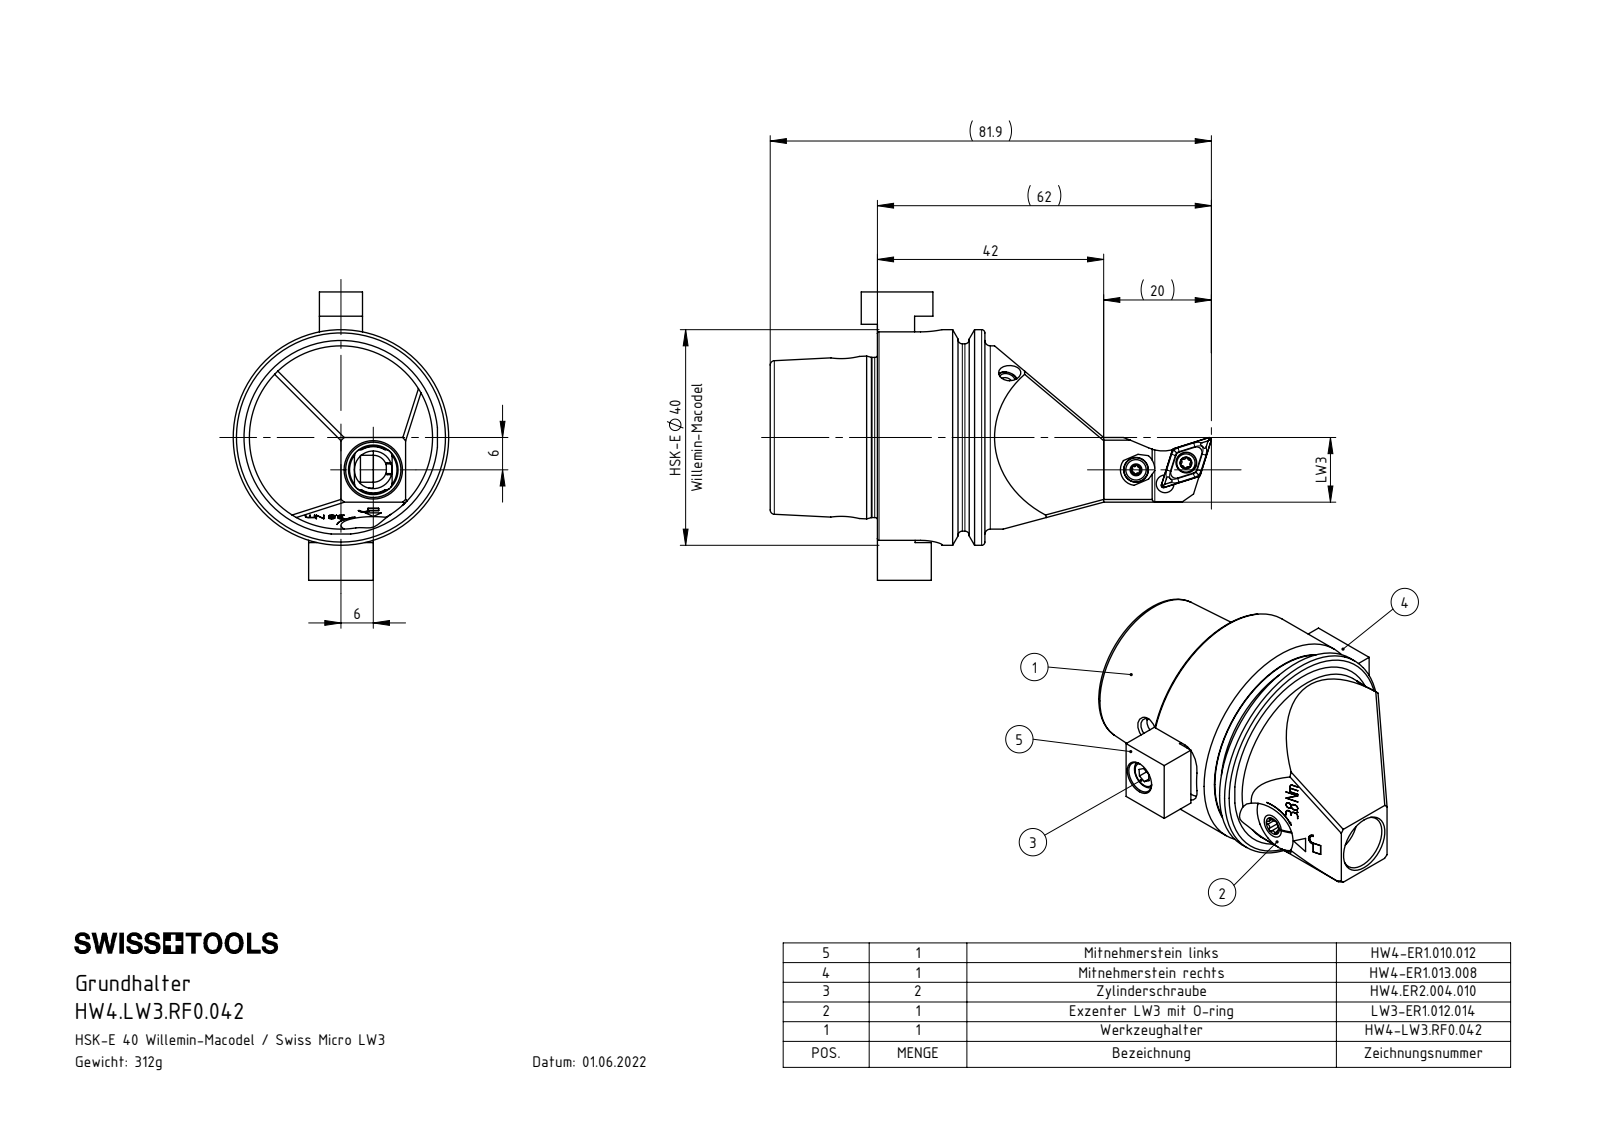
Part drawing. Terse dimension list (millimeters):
name: HW4-ER1.010.012_A; LW3-ER1.012.014_C_Standard<Wie bearbeitet>; HW4-ER2.004.010_A; HW4.LW3.RF0.042 (+5 more)
written by: SolidWorks 2017 (AUTOMOTIVE_DESIGN)
unit: mm
bodies: 10 solids, 385 faces (112 planar, 125 cylindrical, 148 other)
size: 61.9 × 53.5 × 40
volume: 37 272 mm³; area: 14 966 mm²
holes: 3× ⌀3.3, 1× ⌀1, 1× ⌀2.4, 1× ⌀3, 1× ⌀4, 1× ⌀4.2, 1× ⌀4.6, 1× ⌀5, 1× ⌀6, 1× ⌀7, 1× ⌀9.21, 1× ⌀11
bosses: 2× ⌀4, 1× ⌀40, 1× ⌀34.75, 1× ⌀34, 1× ⌀29.7, 1× ⌀11.4, 1× ⌀9.5, 1× ⌀7.7
rounds: 6× R0.34, 6× R0.59, 4× R1.3, 3× R4, 2× R2.5, 1× R3.6, 1× R3.7, 1× R3.75
face distances: 12, 10, 2, 7.95, 19.9, 27.85, 39.85, 19.95, 9, 44.5
hole spacings: 8.49, 9.5, 23.29, 32.56
